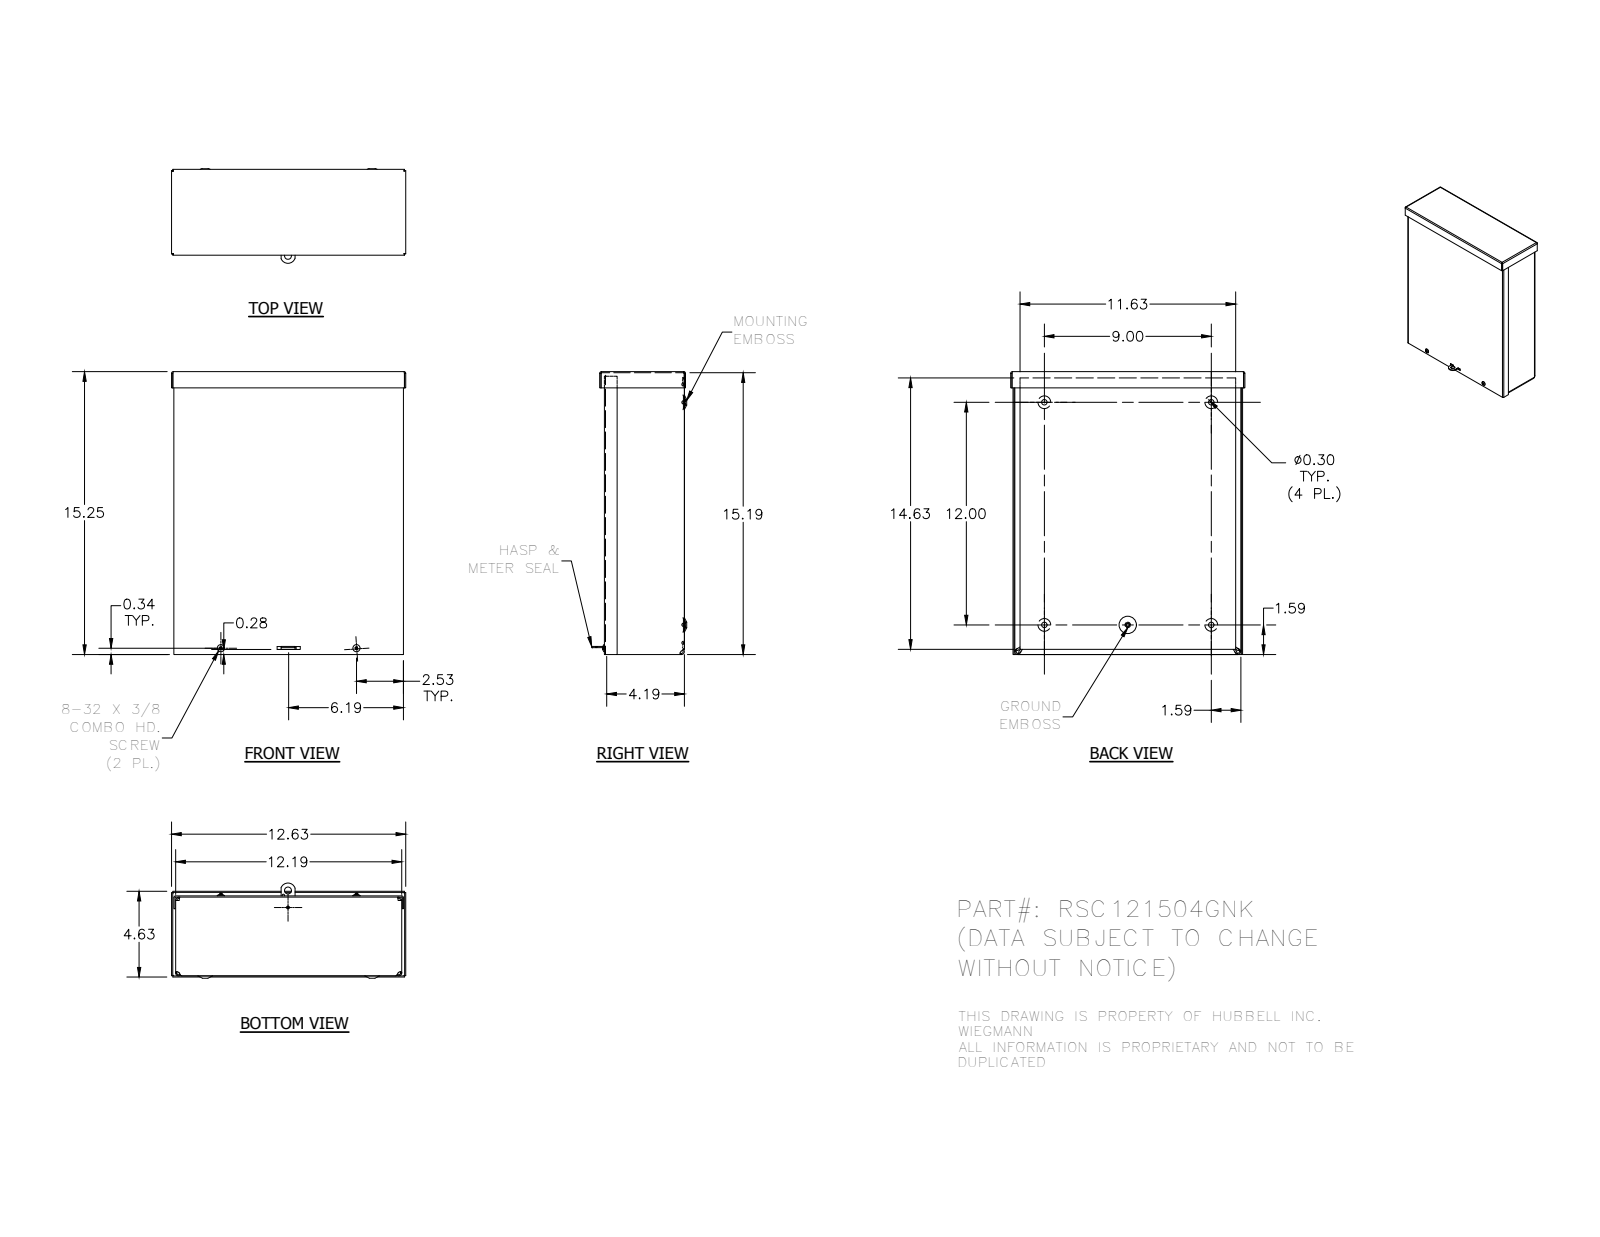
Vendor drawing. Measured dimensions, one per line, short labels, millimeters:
name: RSC121504GNK_WRAP; RSC1215GNK_LID; RSC1204GNK_CAP; 3183 (+3 more)
written by: Autodesk Inventor 2014 (AUTOMOTIVE_DESIGN)
unit: mm
bodies: 7 solids, 377 faces (163 planar, 78 cylindrical, 136 other)
size: 387.36 × 320.68 × 130.17
volume: 776 107 mm³; area: 996 304 mm²
holes: 4× ⌀7.62, 4× ⌀7.95, 2× ⌀3.17, 2× ⌀3.76, 1× ⌀3.96, 1× ⌀4.19, 1× ⌀9.52
bosses: 2× ⌀9.75, 2× ⌀4.17, 1× ⌀5.8
rounds: 8× R0.79, 8× R2.37, 8× R3.17, 8× R4.75, 4× R1.4, 4× R1.57, 4× R2.38, 4× R2.97
face distances: 1.58, 107.93, 106.35, 1.59, 109.52, 107.94, 1.57, 307.99, 384.19, 3.15
hole spacings: 34.43, 114.3, 185.75, 228.6, 304.8, 325.52, 332.44, 337.26
